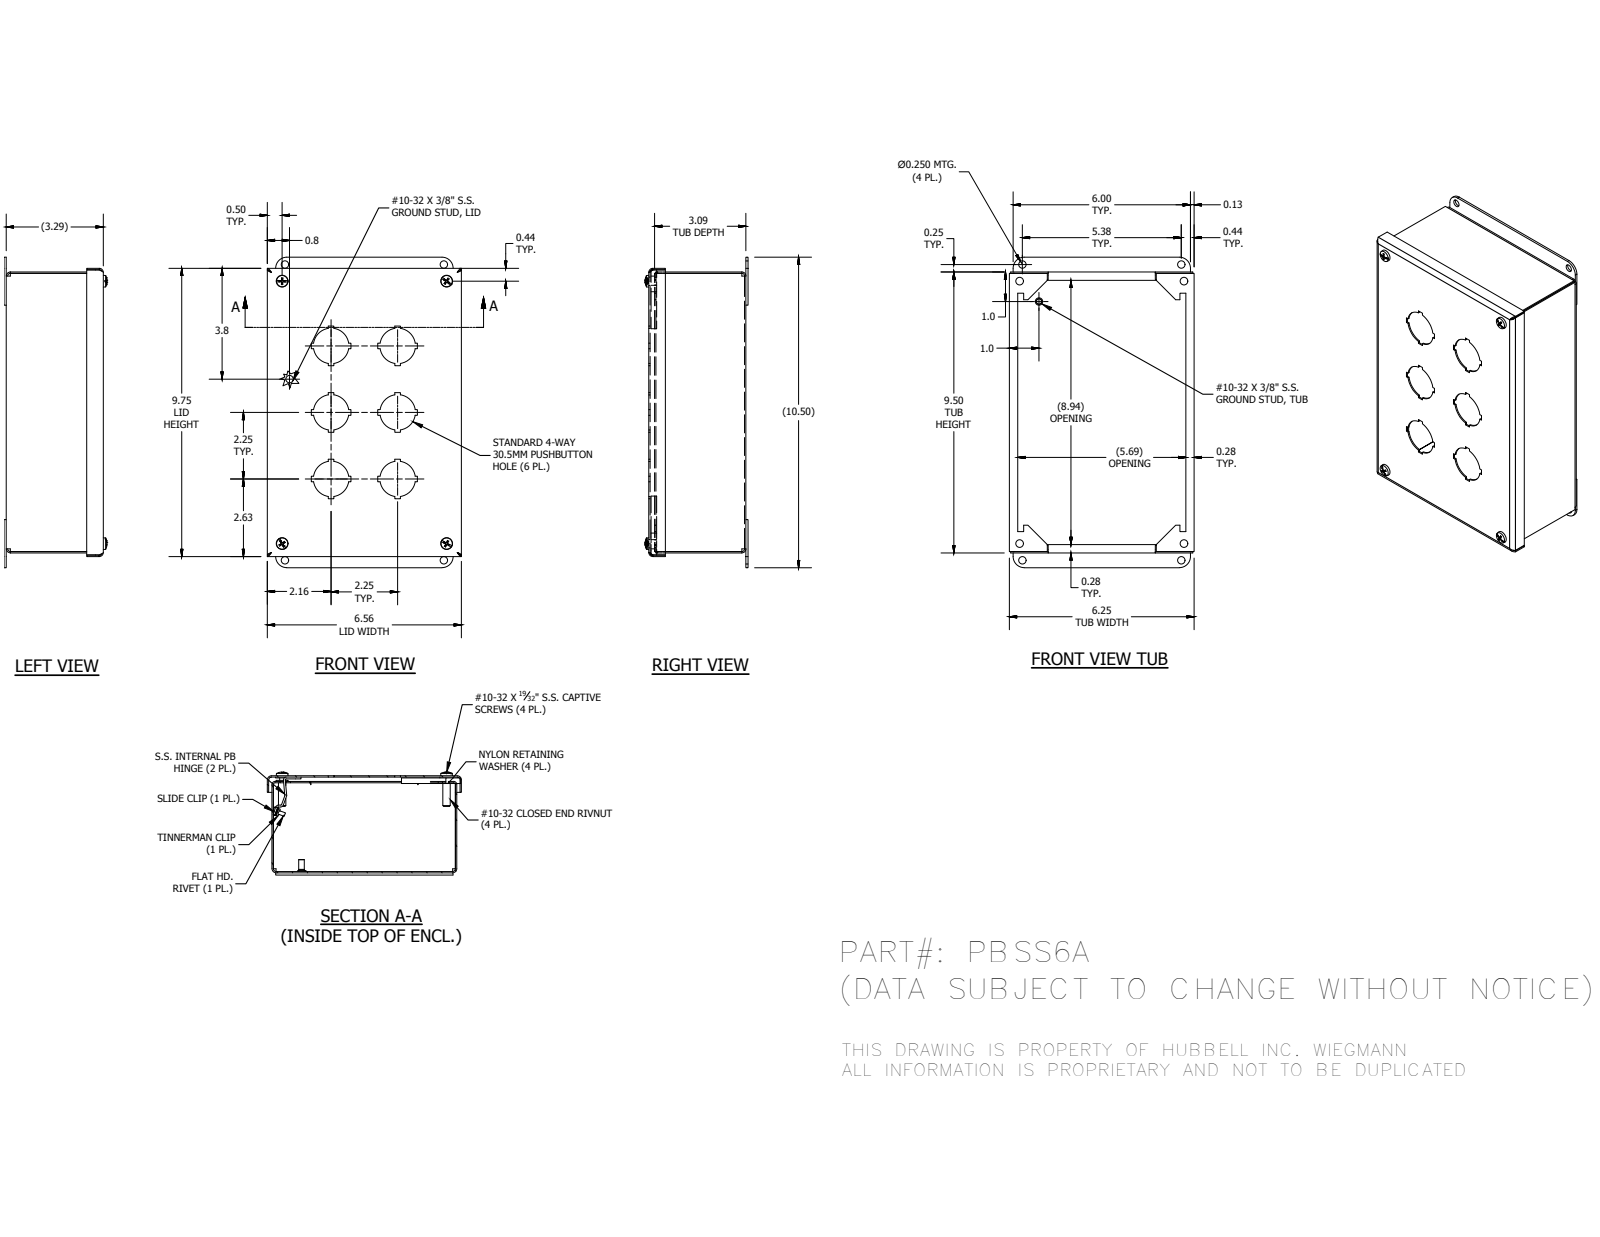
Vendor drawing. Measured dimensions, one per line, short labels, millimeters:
name: PBSS6ALID; 37210; 39077; PBSS6ABKP (+8 more)
written by: Autodesk Inventor 2016 (AUTOMOTIVE_DESIGN)
unit: mm
bodies: 25 solids, 735 faces (473 planar, 154 cylindrical, 108 other)
size: 266.7 × 166.69 × 88.41
volume: 215 280 mm³; area: 349 708 mm²
holes: 6× ⌀30.48, 4× ⌀3.96, 4× ⌀4.98, 4× ⌀6.35, 4× ⌀6.53, 4× ⌀7.06, 4× ⌀7.14, 2× ⌀3.38, 2× ⌀3.56, 2× ⌀7.95
bosses: 4× ⌀11.51, 4× ⌀10.31, 4× ⌀6.3, 4× ⌀4.25, 3× ⌀6.35, 2× ⌀4.83, 1× ⌀3.17
rounds: 8× R2.38, 8× R3.52, 6× R4.78, 4× R1.59, 4× R2.27, 4× R2.29, 4× R2.73, 4× R9.53
face distances: 1.14, 1.15, 81.15, 82.3, 82.29, 83.44, 240.16, 157.6, 158.75, 156.46
hole spacings: 57.15, 80.34, 80.82, 133.06, 174.99, 188.38, 239.72, 0.48
